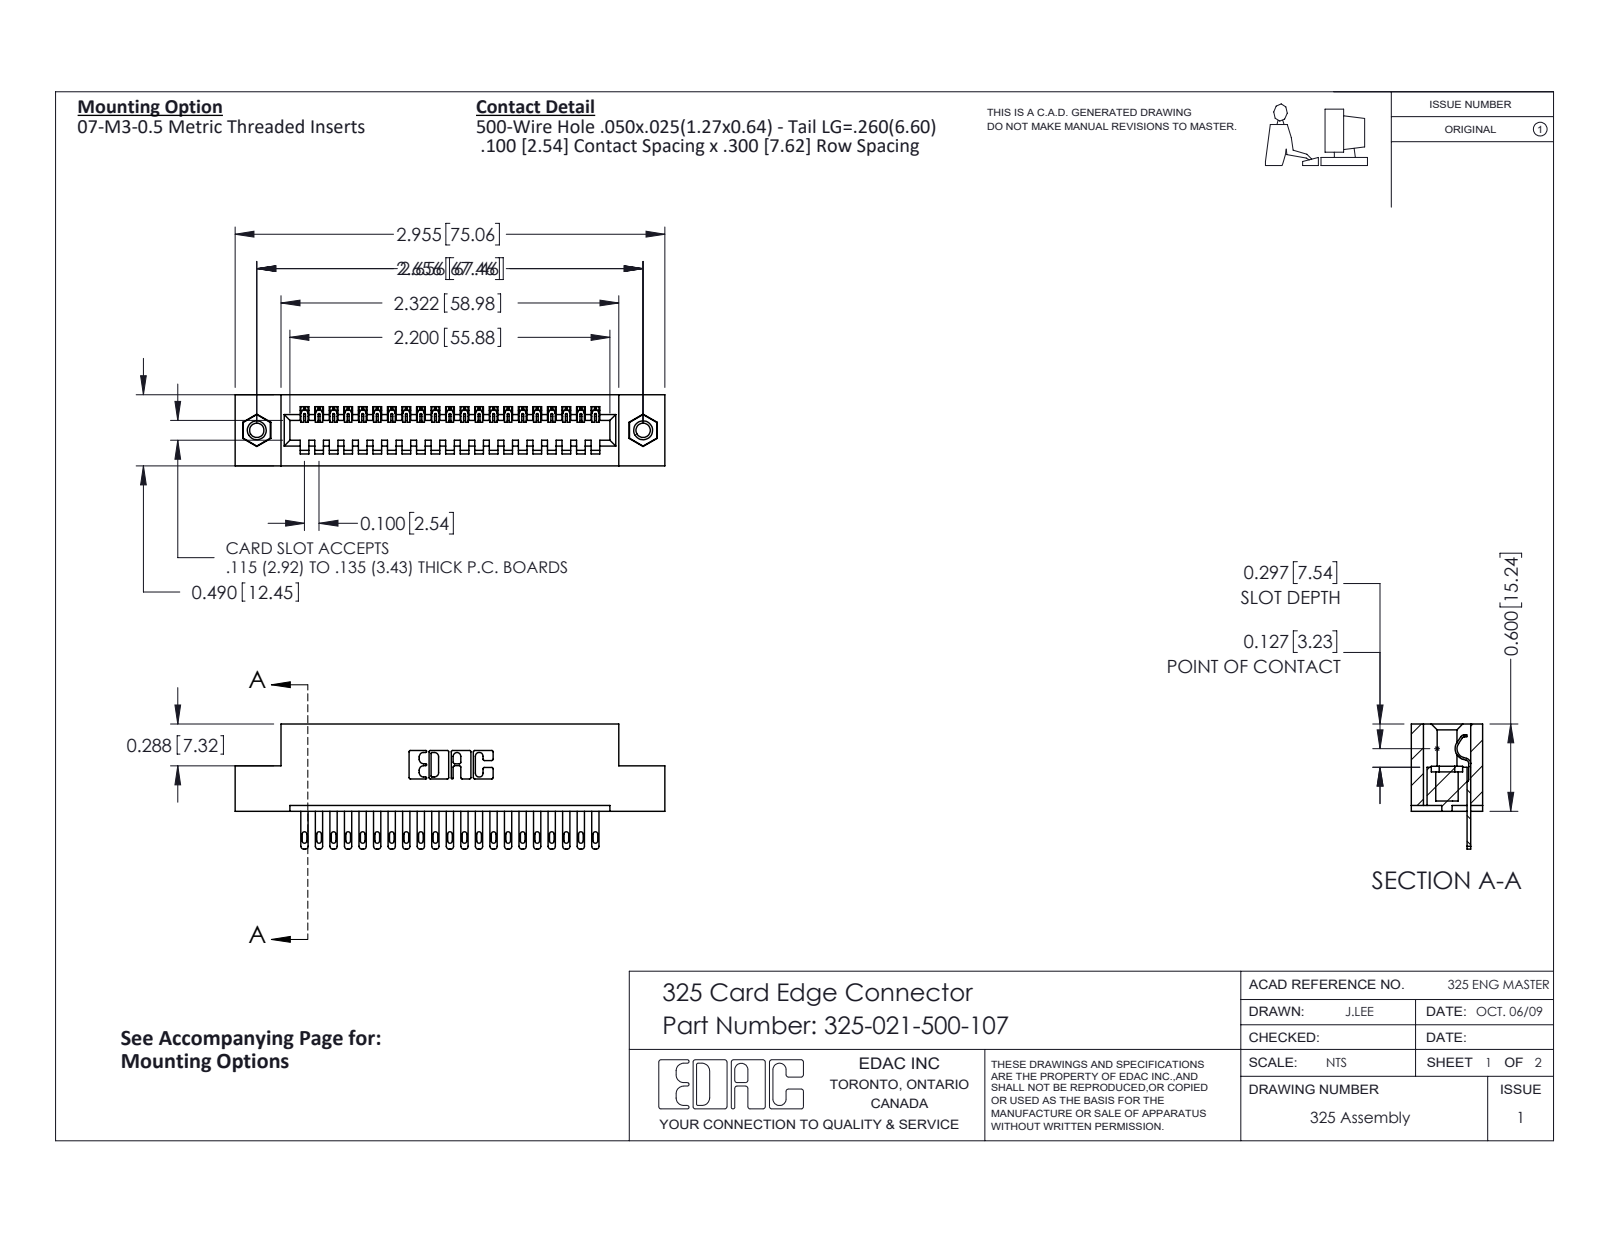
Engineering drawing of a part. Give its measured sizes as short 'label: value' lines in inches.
name: 325-021-500-107; 325-292-001_325-293-100; 345-250-001_345-250-005-103; 325 Part_TI
written by: SolidWorks 2016 (CONFIG_CONTROL_DESIGN)
unit: in
bodies: 24 solids, 1308 faces (858 planar, 434 cylindrical, 16 other)
size: 2.955 × 0.86 × 0.49
volume: 0.571 in³; area: 15.42 in²
holes: 2× ⌀0.098, 2× ⌀0.125, 2× ⌀0.16
bosses: 2× ⌀0.155
rounds: 42× R0.006, 42× R0.016, 42× R0.02, 22× R0.01, 6× R0.007, 6× R0.031, 3× R0.026, 1× R0.014
face distances: 0.083, 0.407, 0.3, 0.49, 0.107, 0.383, 0.025, 0.6, 0.04, 0.1
hole spacings: 2.656
